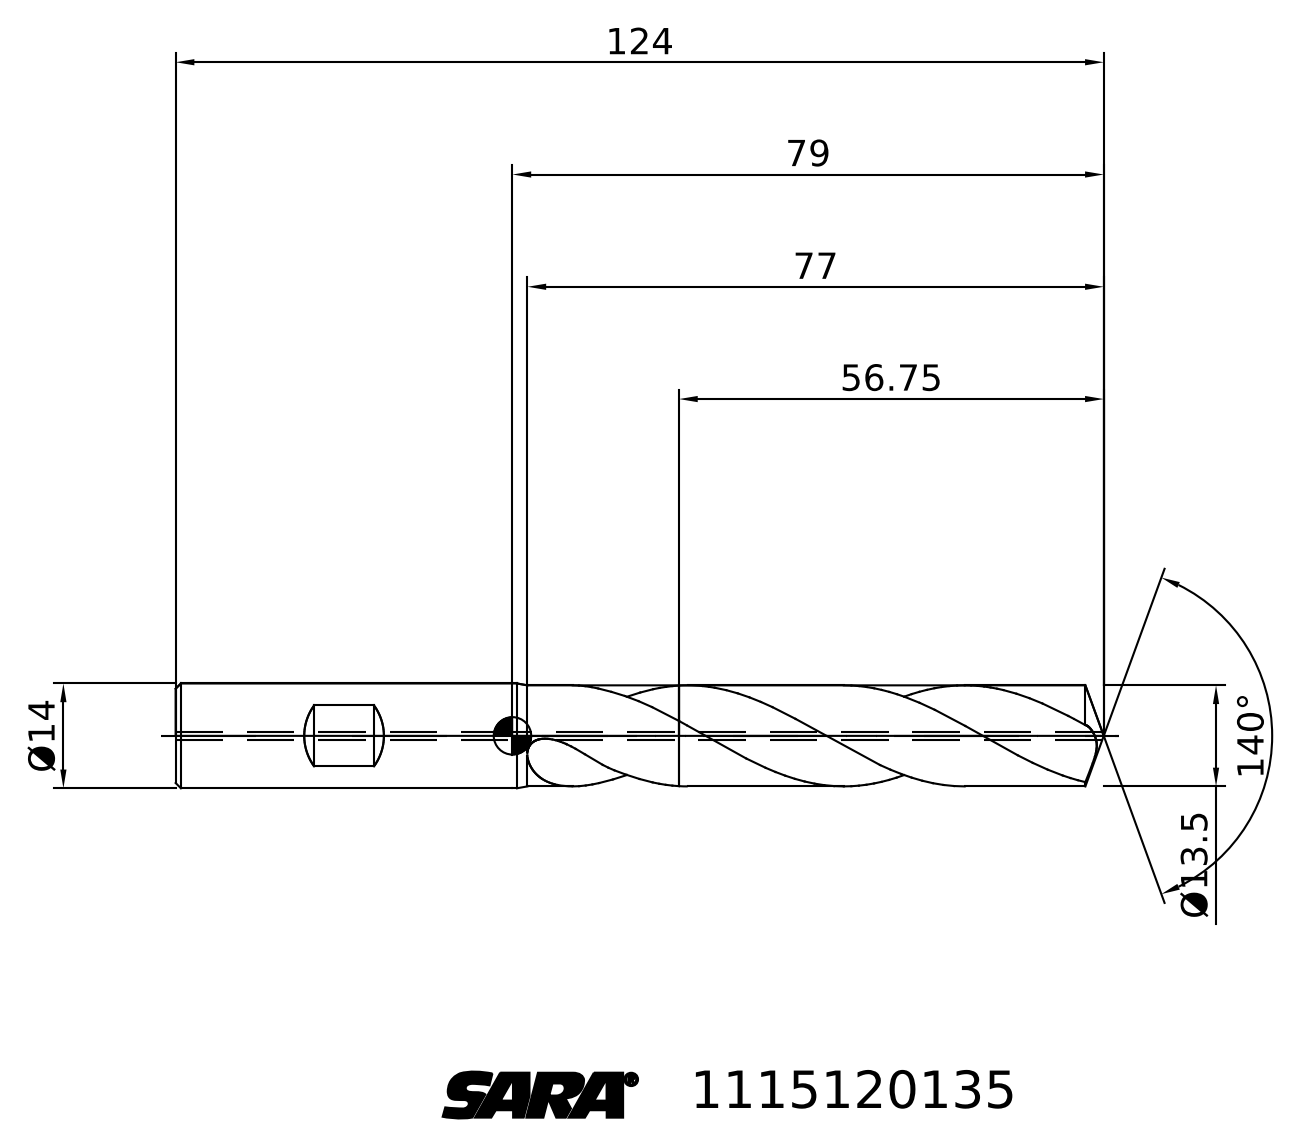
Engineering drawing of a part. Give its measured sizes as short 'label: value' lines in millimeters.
written by: TDM (AUTOMOTIVE_DESIGN)
unit: mm
bodies: 2 solids, 29 faces (6 planar, 0 cylindrical, 23 other)
size: 124 × 17.75 × 14
volume: 14 446 mm³; area: 5 956 mm²
face distances: 67.25
